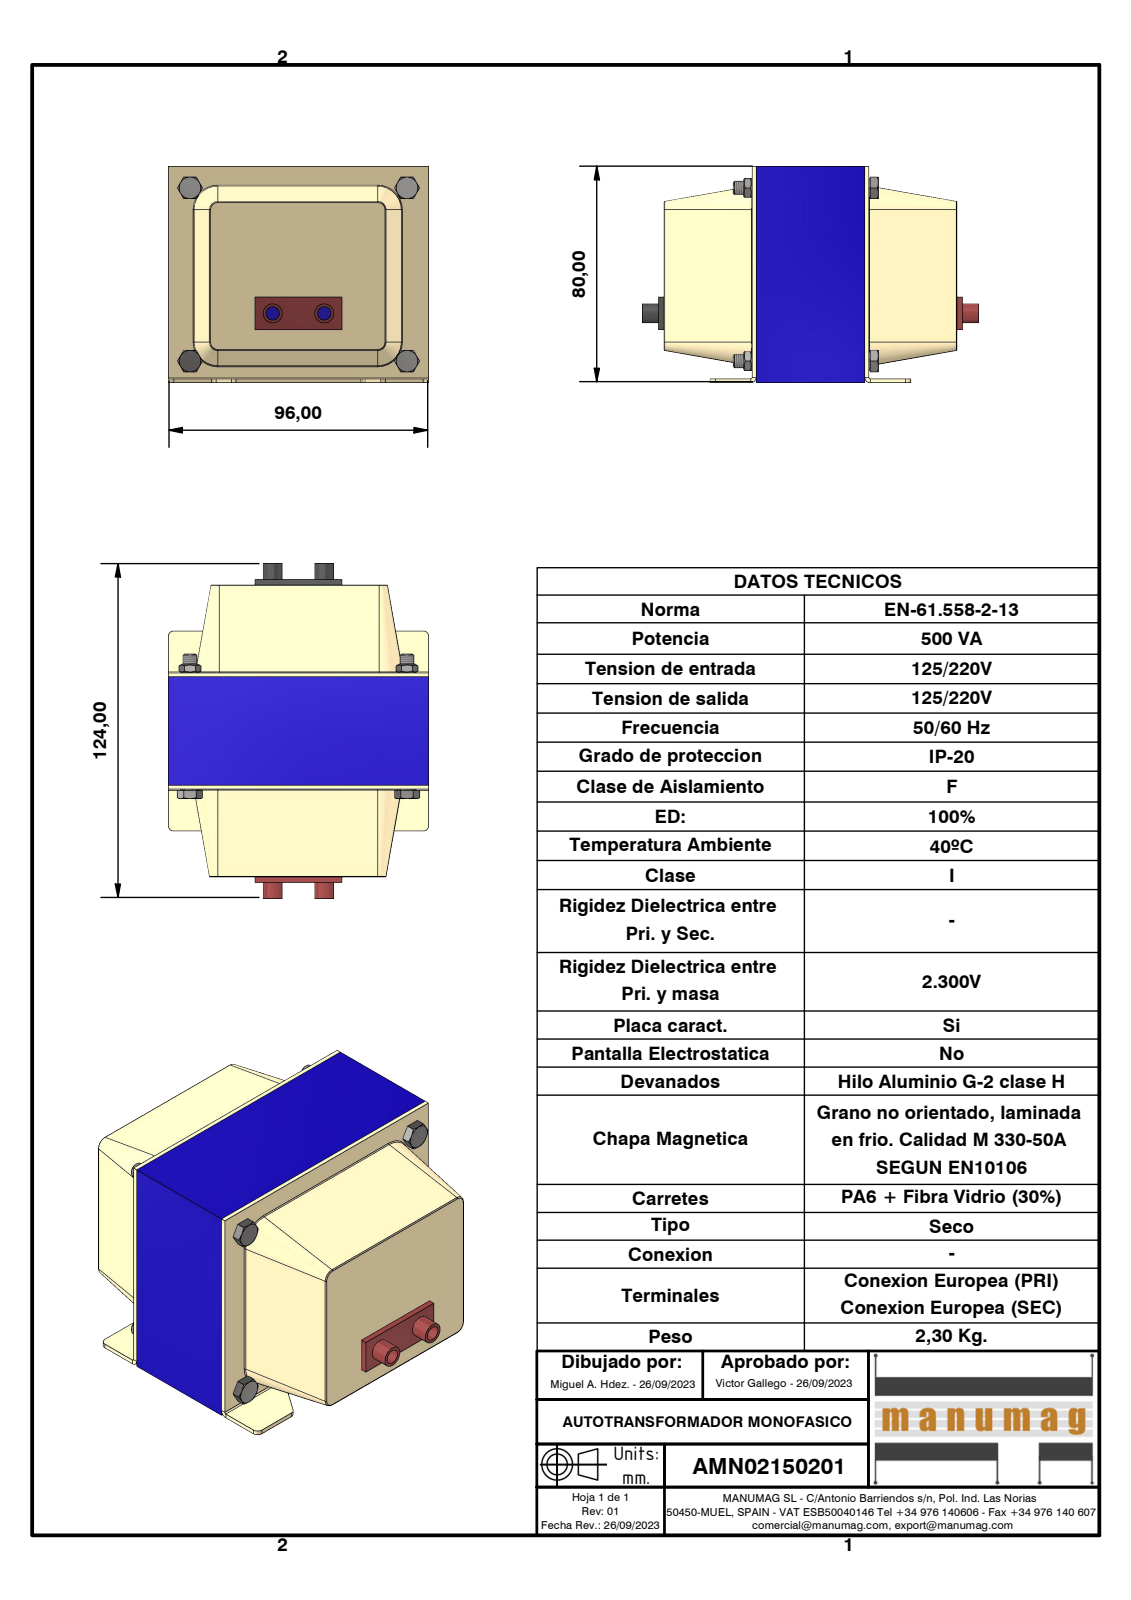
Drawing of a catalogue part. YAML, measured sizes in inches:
part_name: "AMN02150201; EI96 x 80 - 40 (RC32) Azul; TAPA RC32 RECEPTACULO; Receptaculo Rojo (+3 more)"
step_written_by: "Autodesk Inventor 2023 (AUTOMOTIVE_DESIGN)"
units: inches
bodies: {solids: 13, faces: 310, planar: 162, cylindrical: 68, other: 80}
overall_size: [4.882, 3.78, 3.15]
volume: 16.67
surface_area: 167.4
round_holes:
  - {diameter: 0.197, count: 6}
  - {diameter: 0.128, count: 4}
  - {diameter: 0.217, count: 4}
round_bosses_or_shafts:
  - {diameter: 0.264, count: 4}
  - {diameter: 0.18, count: 4}
  - {diameter: 0.276, count: 2}
partial_cylinders:
  - {radius: 0.015, count: 16}
  - {radius: 0.079, count: 14}
  - {radius: 0.02, count: 2}
face_to_face_distances: [0.059, 2.913, 1.28, 0.63, 2.52, 1.575, 3.15, 1.339, 4.193, 2.854]
hole_center_spacings: [1.387, 2.069, 2.185, 2.52, 2.67, 3.15, 4.033, 0.748]
